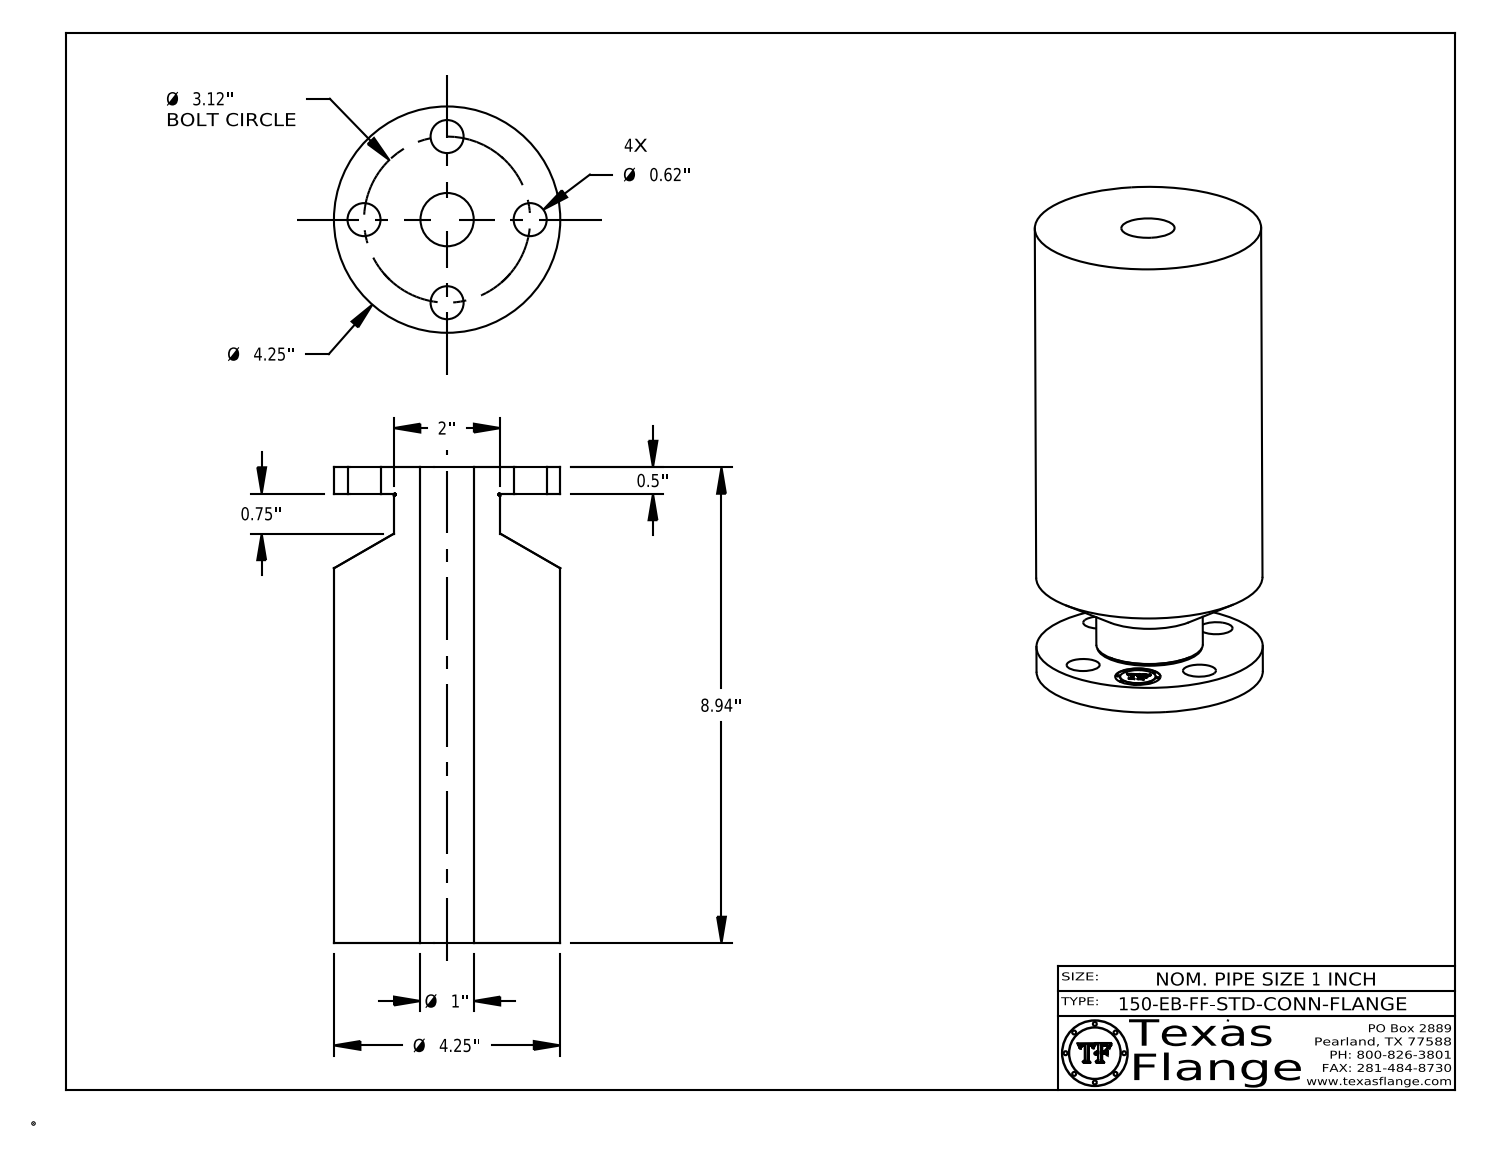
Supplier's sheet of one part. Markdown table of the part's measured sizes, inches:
| quantity | value |
| --- | --- |
| part name | 1-150-EB-FF-STD-CONN-FLANGE |
| STEP written by | CATIA V5 STEP AP214 (AUTOMOTIVE_DESIGN) |
| units | inches |
| bodies | 1 solid, 410 faces (368 planar, 36 cylindrical, 6 other) |
| overall size | 8.938 × 4.25 × 4.25 |
| volume | 106.9 in³ |
| surface area | 185.8 in² |
| round holes (diameter × count) | 0.62 × 4, 0.85 × 1, 1 × 1 |
| round bosses / shafts (diameter × count) | 0.051 × 8, 4.25 × 1, 2 × 1, 0.67 × 1 |
| main face-to-face distances | 8.937, 0.498, 8.44, 0.493, 8.445, 0.254, 0.248, 0.016, 0.046, 0.165 |
| hole center spacings | 1.56, 2.206, 1.194, 2.882, 3.12, 1.56 |
